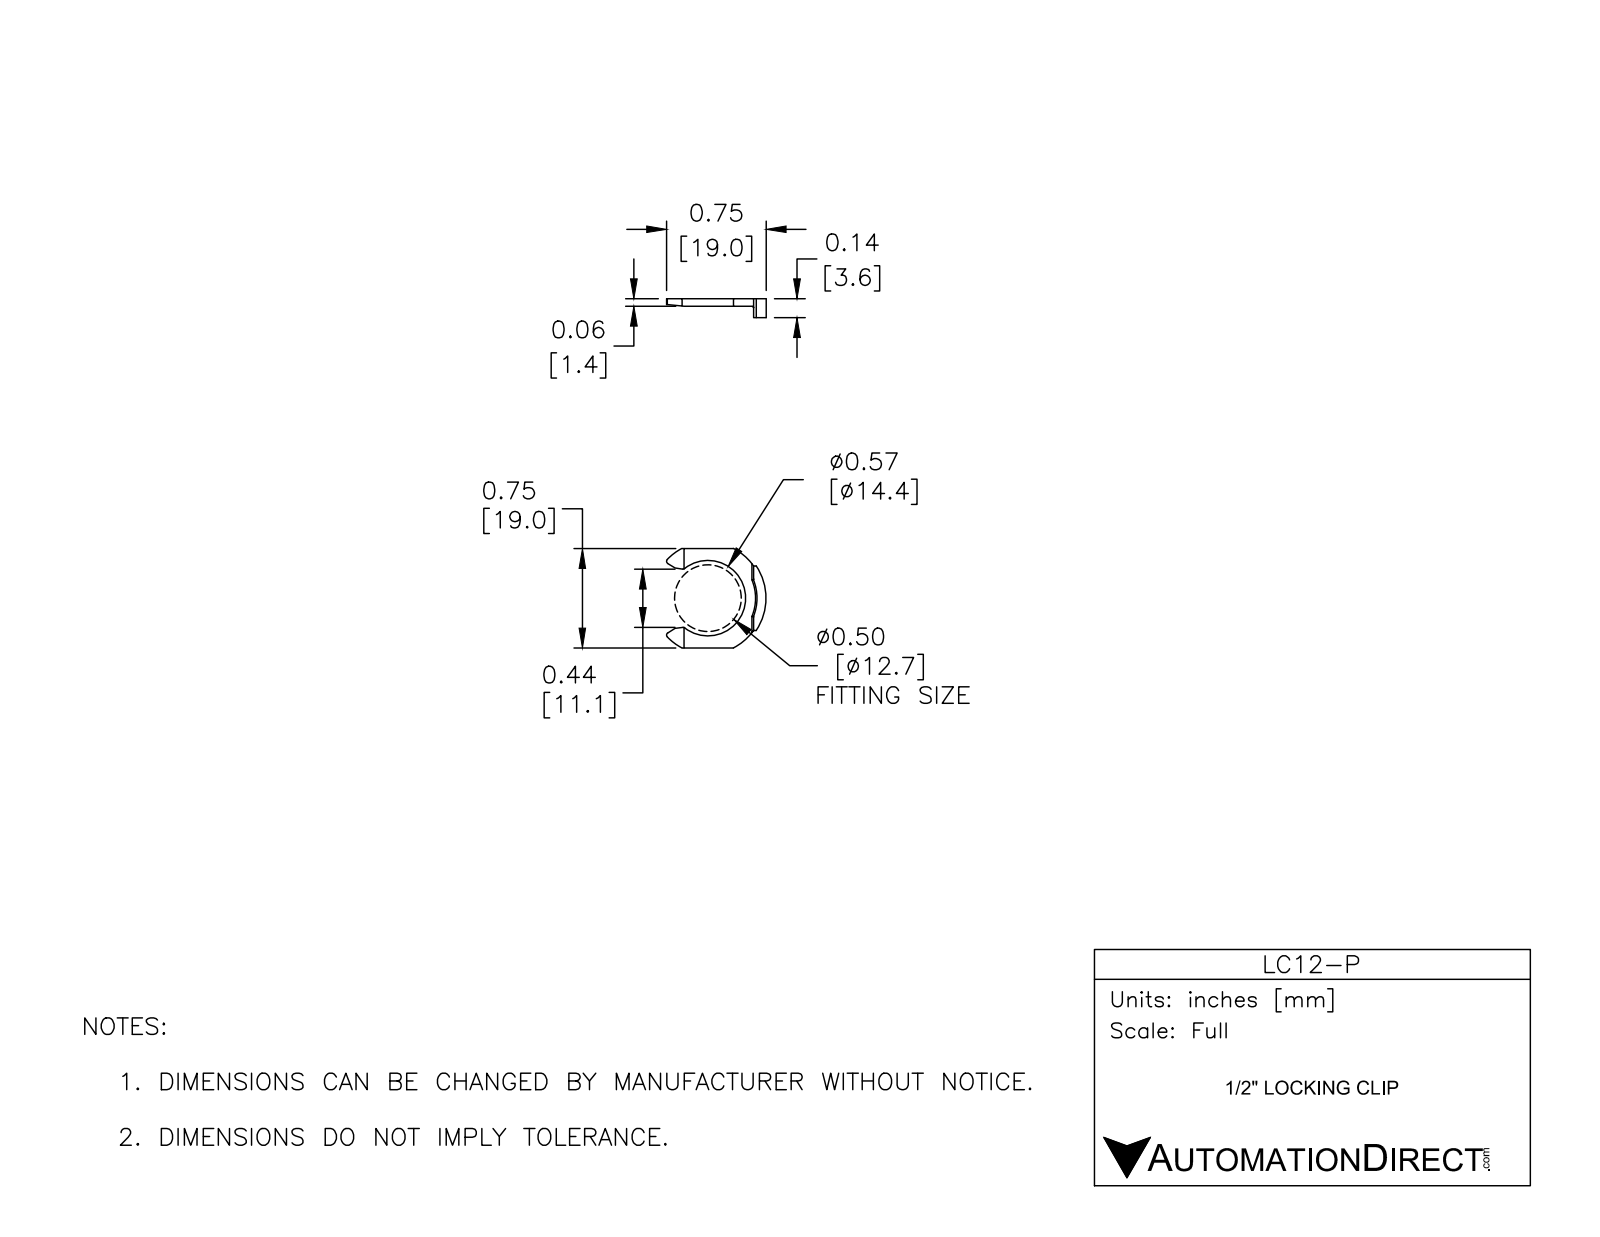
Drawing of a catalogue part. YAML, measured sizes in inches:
part_name: "LC12-P"
step_written_by: "SolidWorks 2017 (AUTOMOTIVE_DESIGN)"
units: inches
bodies: {solids: 1, faces: 32, planar: 15, cylindrical: 16, other: 1}
overall_size: [0.749, 0.748, 0.142]
volume: 0.014
surface_area: 0.716
partial_cylinders:
  - {radius: 0.02, count: 4}
  - {radius: 0.012, count: 1}
  - {radius: 0.283, count: 1}
  - {radius: 0.37, count: 1}
  - {radius: 0.42, count: 1}
  - {radius: 0.422, count: 1}
  - {radius: 0.437, count: 1}
face_to_face_distances: [0.055, 0.142, 0.087, 0.748, 0.131, 0.617, 0.487]
